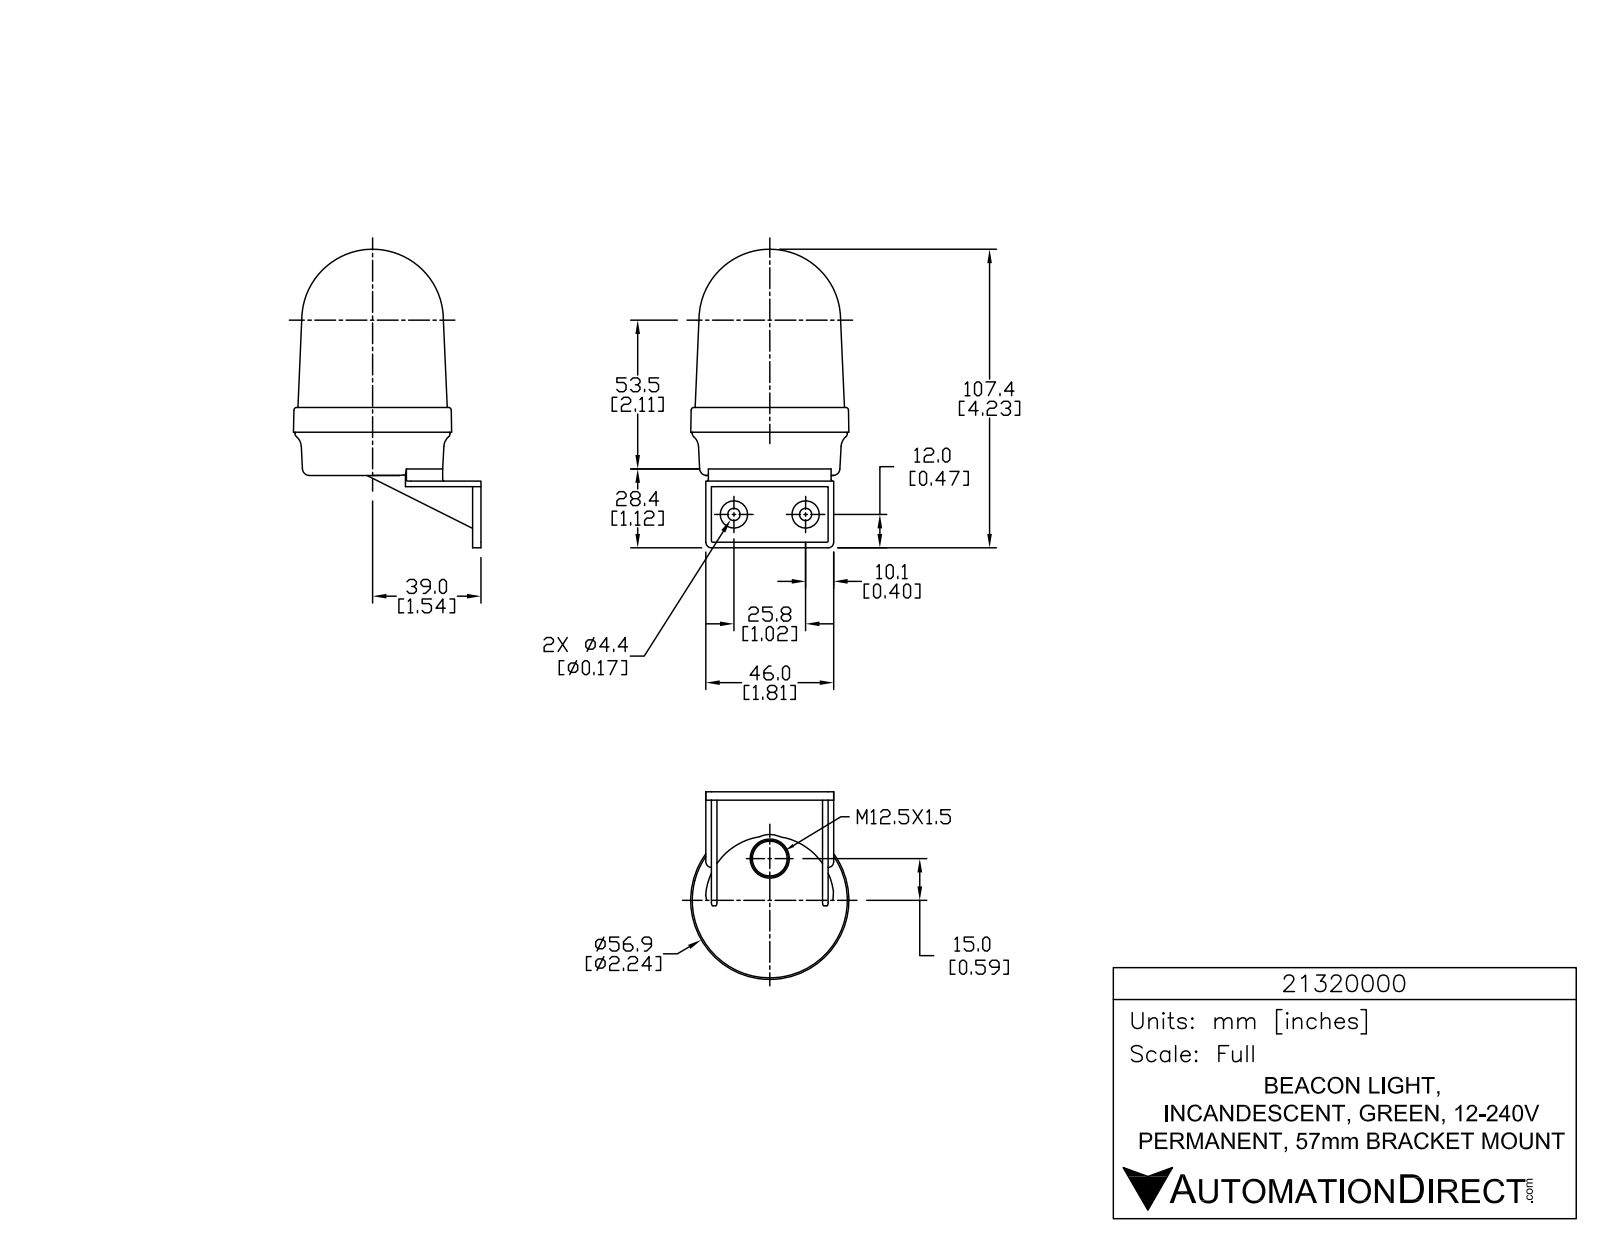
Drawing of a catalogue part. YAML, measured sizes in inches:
part_name: "21320000"
step_written_by: "SolidWorks 2015 (AUTOMOTIVE_DESIGN)"
units: inches
bodies: {solids: 1, faces: 826, planar: 550, cylindrical: 178, other: 98}
overall_size: [4.228, 2.838, 2.392]
volume: 9.936
surface_area: 32.97
round_holes:
  - {diameter: 0.039, count: 3}
  - {diameter: 0.173, count: 2}
round_bosses_or_shafts:
  - {diameter: 0.226, count: 3}
  - {diameter: 0.056, count: 3}
  - {diameter: 0.386, count: 2}
  - {diameter: 2.197, count: 1}
partial_cylinders:
  - {radius: 0.008, count: 6}
  - {radius: 0.008, count: 6}
  - {radius: 0.008, count: 6}
  - {radius: 0.02, count: 6}
  - {radius: 0.131, count: 6}
  - {radius: 0.079, count: 4}
  - {radius: 0.004, count: 3}
  - {radius: 0.005, count: 3}
face_to_face_distances: [0.079, 0.157, 1.575, 1.654, 0.039, 0.118, 1.496, 0.866, 0.945, 0.772]
hole_center_spacings: [1.016]
